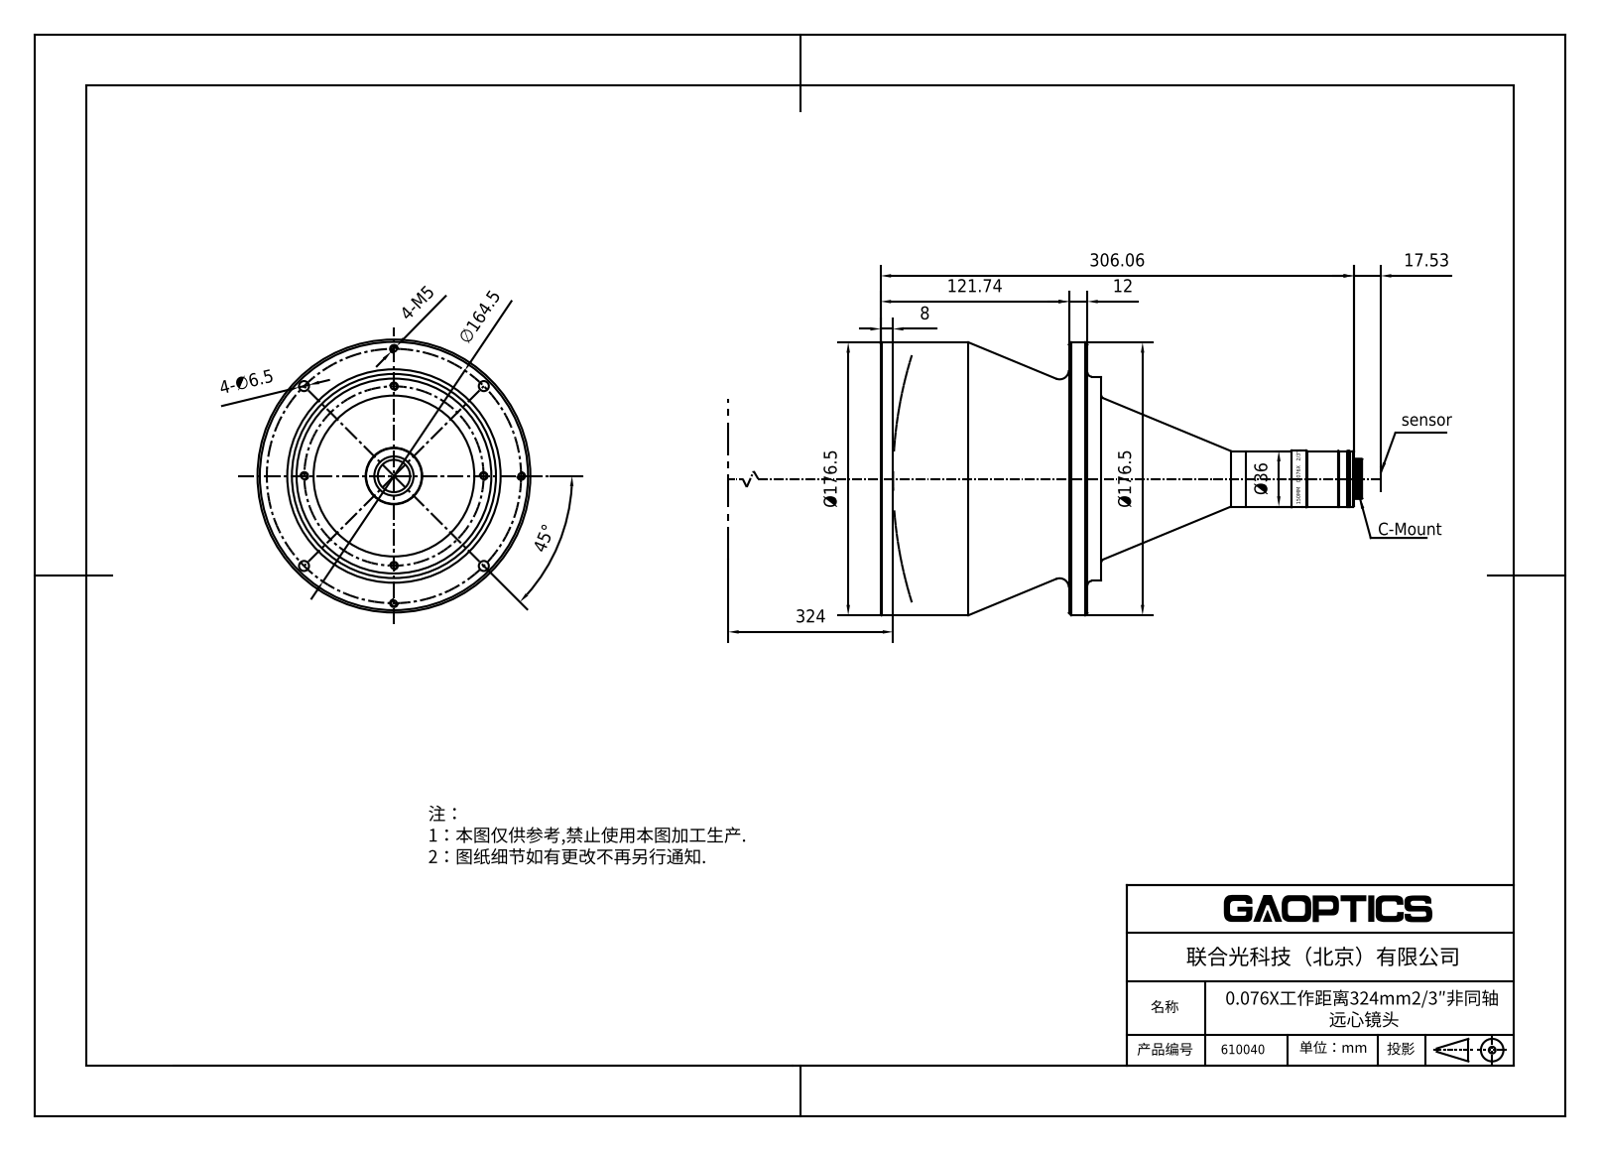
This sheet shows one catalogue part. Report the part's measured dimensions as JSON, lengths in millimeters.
{"part_name": "610040", "step_written_by": "SolidWorks 2020 (CONFIG_CONTROL_DESIGN)", "units": "millimeters", "bodies": {"solids": 0, "faces": 305, "planar": 44, "cylindrical": 157, "other": 104}, "overall_size": [311.6, 176.5, 176.5], "round_holes": [[4, 4], [7.5, 4], [2.2, 3], [3, 3], [16.5, 1], [18.9, 1], [21.9, 1], [24.6, 1], [25.8, 1], [28, 1], [29.4, 1], [31.8, 1]], "round_bosses_or_shafts": [[6.5, 4], [5, 4], [168.1, 1], [165.3, 1], [160.5, 1], [145, 1], [143, 1], [105, 1]], "face_to_face_distances": [32.98, 113.98, 81, 12, 101.98, 69, 122.98, 90, 21, 9], "hole_center_spacings": [58, 82.02, 14.5, 25.12, 46.01, 52.28, 59.79, 66.45]}
